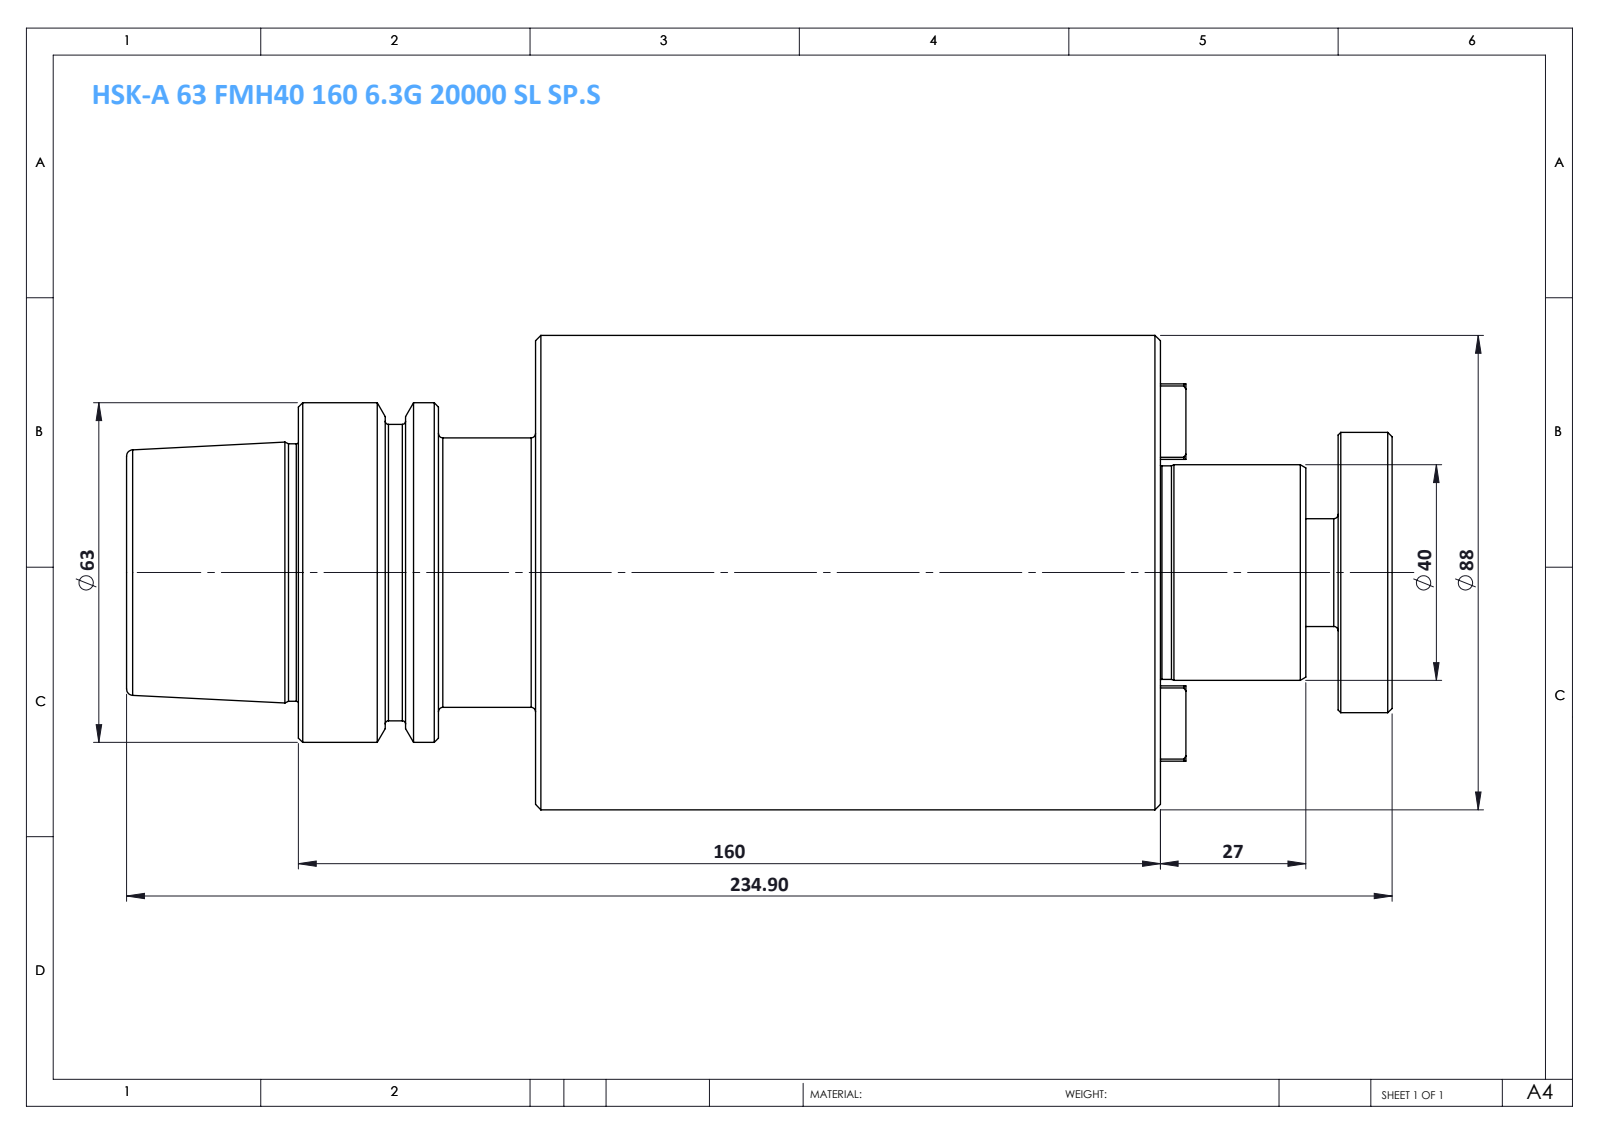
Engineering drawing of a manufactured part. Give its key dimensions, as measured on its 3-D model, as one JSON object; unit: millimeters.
{"part_name": "HSK-A 63 FMH40 160 6.3G 20000 SL SP.S", "step_written_by": "SolidWorks 2014 (CONFIG_CONTROL_DESIGN)", "units": "millimeters", "bodies": {"solids": 1, "faces": 102, "planar": 38, "cylindrical": 20, "other": 44}, "overall_size": [234.9, 88, 88], "volume_mm3": 932069, "surface_area_mm2": 68622, "round_bosses_or_shafts": [[88, 1], [63, 1], [55, 1], [52, 1], [50, 1], [47.78, 1], [40, 1], [39.6, 1]], "face_to_face_distances": [116, 43, 159, 10, 33, 149, 234.9, 224.9, 191.9, 75.9]}
